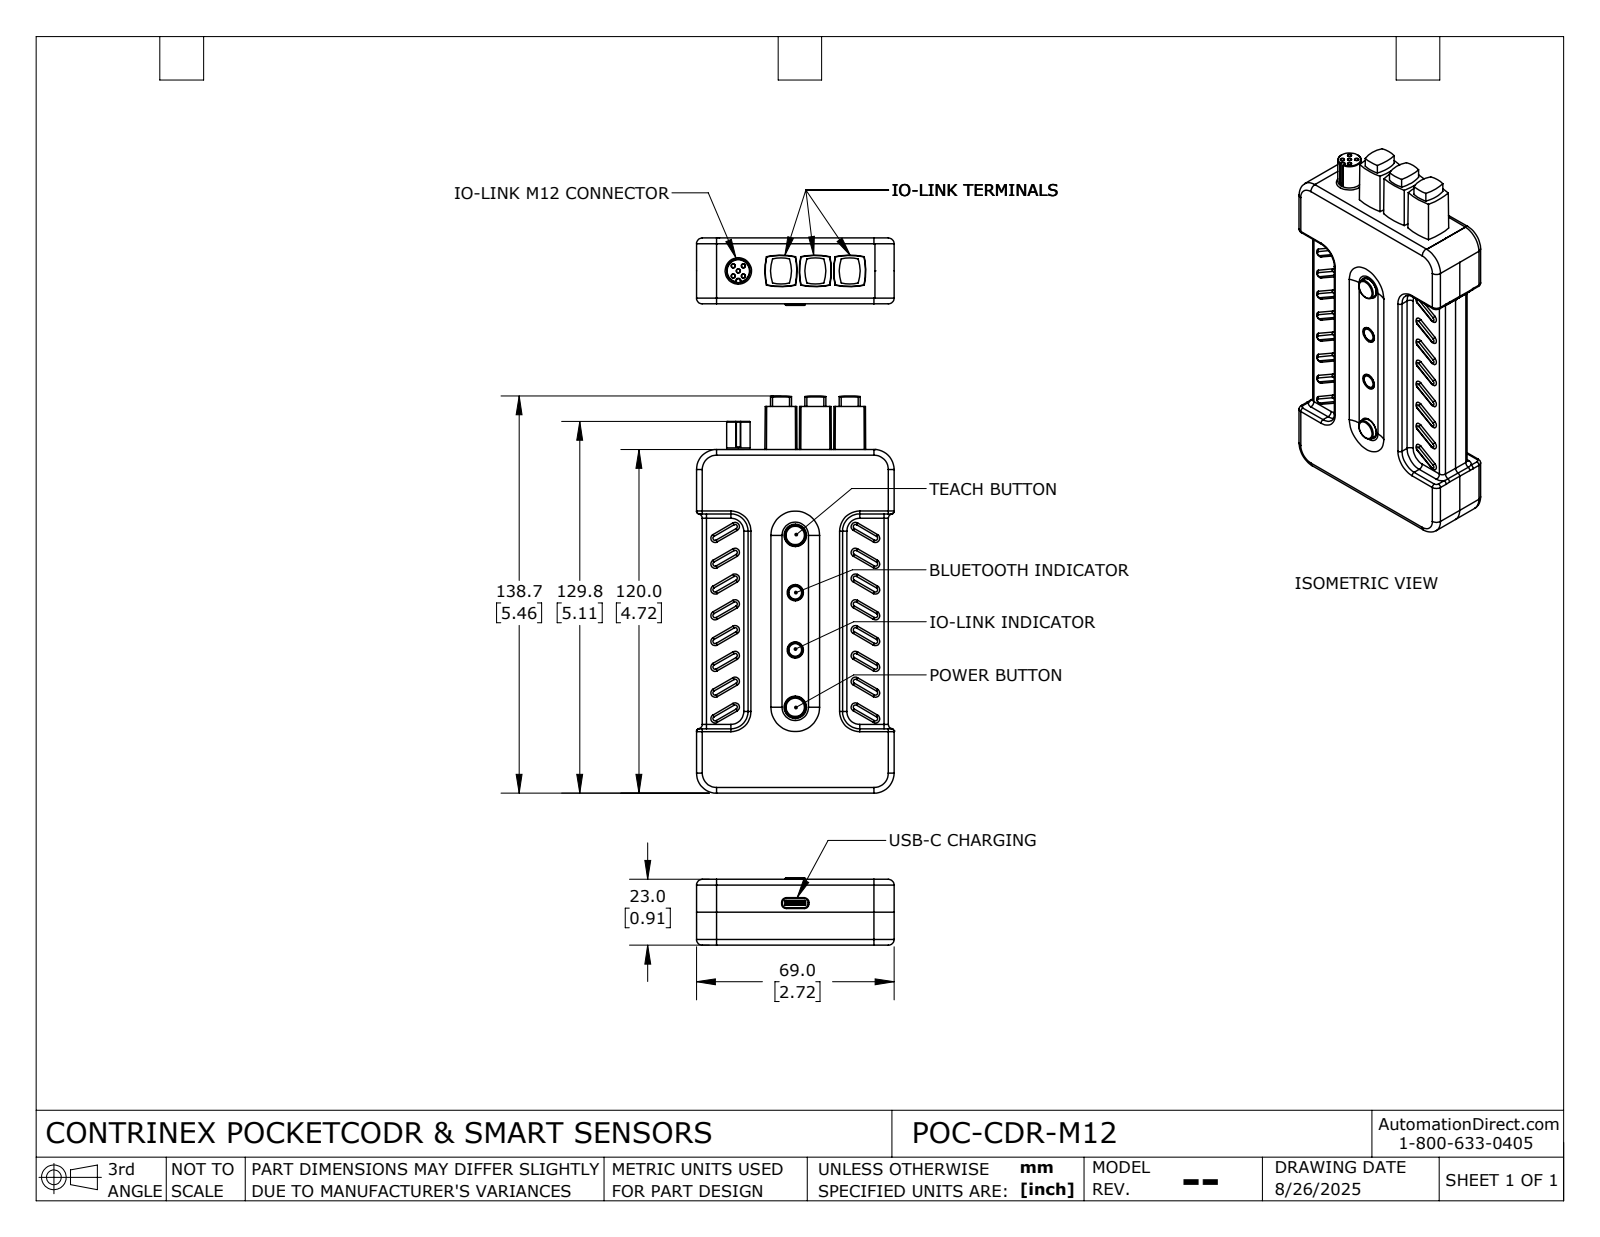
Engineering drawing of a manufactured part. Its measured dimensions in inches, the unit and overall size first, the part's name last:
Units: inches
Overall size (bounding box): 5.461 × 2.717 × 0.925
Round holes (diameter × count): ⌀0.049 ×5
Round bosses / shafts (diameter × count): ⌀0.323 ×1
Partial cylindrical surfaces — rounded edges, fillets, slot ends (radius × count): R0.031 ×64, R0.039 ×16, R0.059 ×16, R0.017 ×12, R0.009 ×8, R0.079 ×8, R0.477 ×6, R0.518 ×6
Main face-to-face distances: 0.906, 0.709, 0.197, 0.512, 0.079, 2.638, 2.559, 4.724, 2.008, 0.63
Hole centre spacings: 0.098, 0.139, 0.197
Volume: 10.01 in³ · Surface area: 41.66 in²
Bodies: 1 solid, 517 faces (148 planar, 197 cylindrical, 172 other)
Part name (STEP PRODUCT): POC-CDR-M12
STEP written by: SolidWorks 2024 (AUTOMOTIVE_DESIGN)
